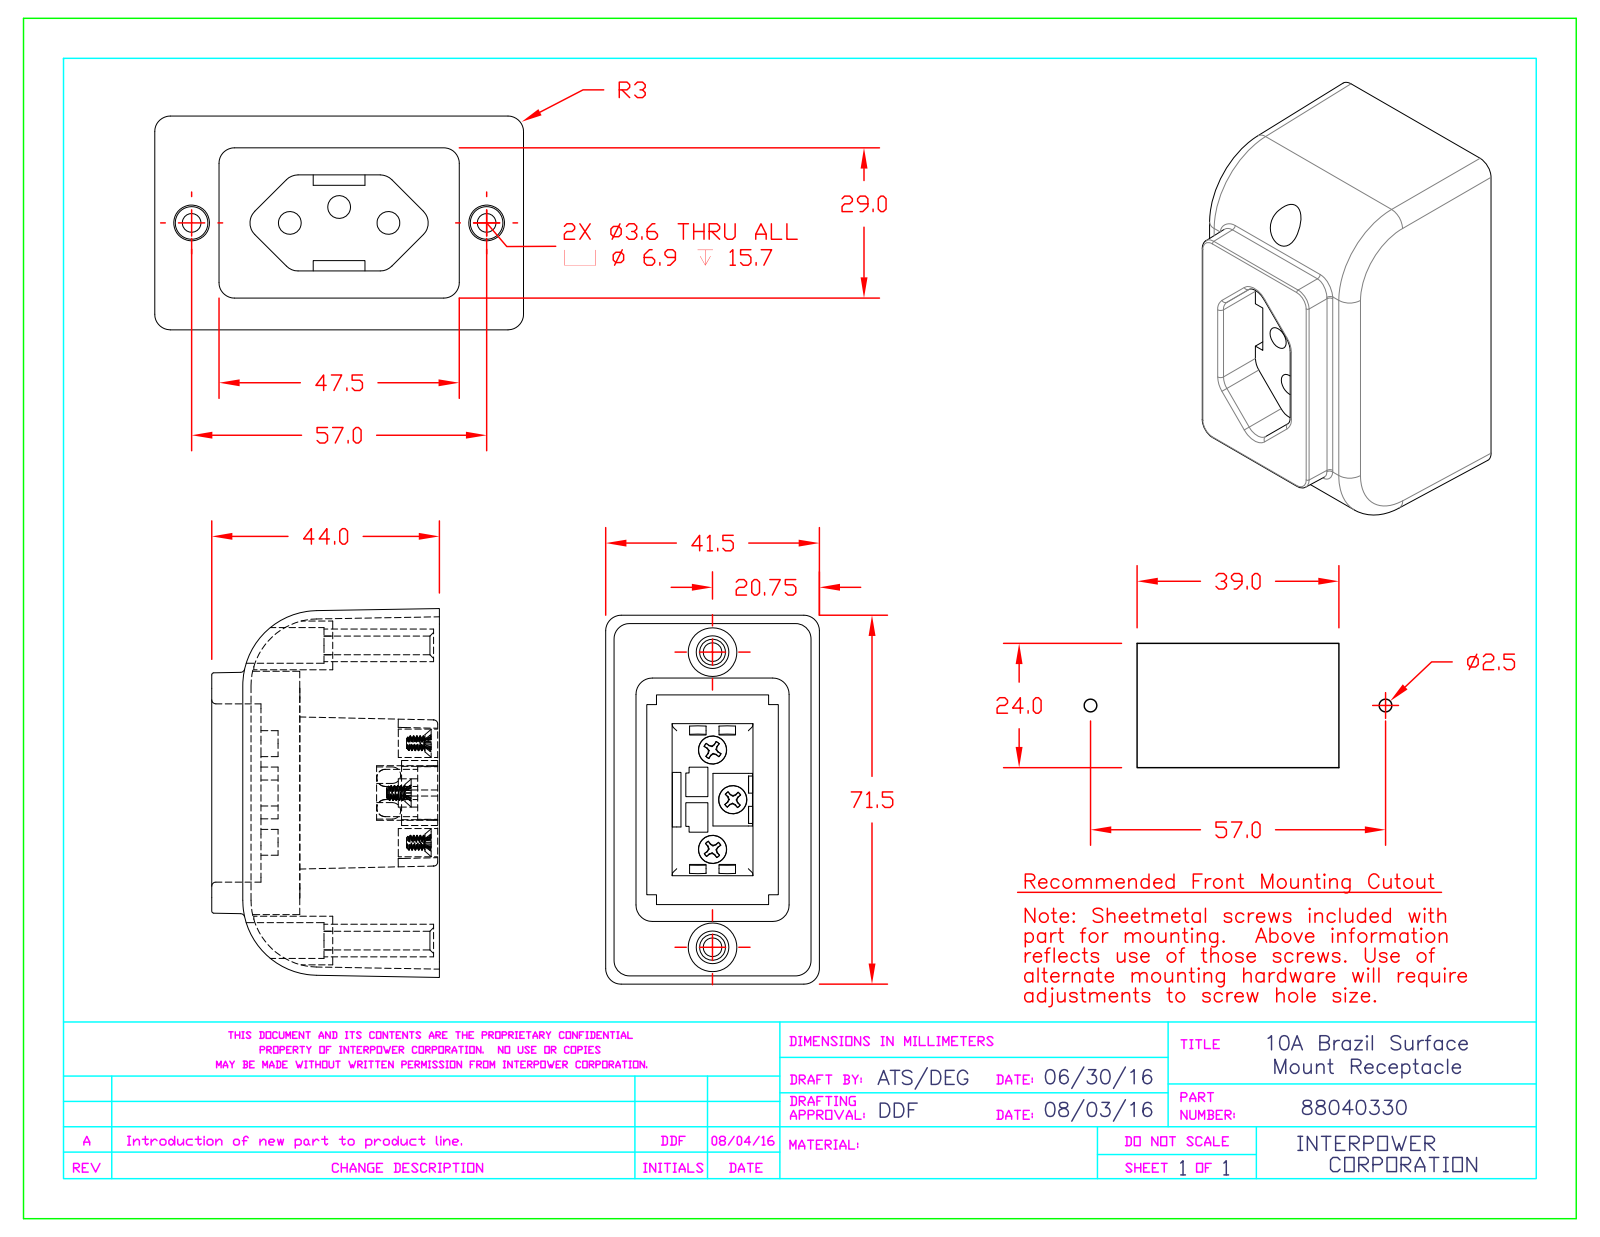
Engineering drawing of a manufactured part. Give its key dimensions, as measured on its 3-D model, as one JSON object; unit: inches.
{"part_name": "88040330", "step_written_by": "SolidWorks 2015 (AUTOMOTIVE_DESIGN)", "units": "inches", "bodies": {"solids": 3, "faces": 252, "planar": 118, "cylindrical": 100, "other": 34}, "overall_size": [2.805, 1.732, 1.625], "volume_in3": 2.689, "surface_area_in2": 44.77, "round_holes": [[0.173, 3], [0.215, 3], [0.142, 2], [0.272, 2]], "round_bosses_or_shafts": [[0.37, 2], [0.248, 2]], "partial_cylinders_radius": [[0.118, 16], [0.031, 14], [0.125, 10], [0.016, 4], [0.063, 4], [0.063, 2], [0.065, 2], [0.508, 2]], "face_to_face_distances": [0.063, 0.67, 0.296, 0.375, 0.148, 0.211, 1.165, 0.294, 0.669, 1.062], "hole_center_spacings": [0.394, 0.397, 0.406, 0.408, 0.744, 0.747, 0.753, 1.128]}
